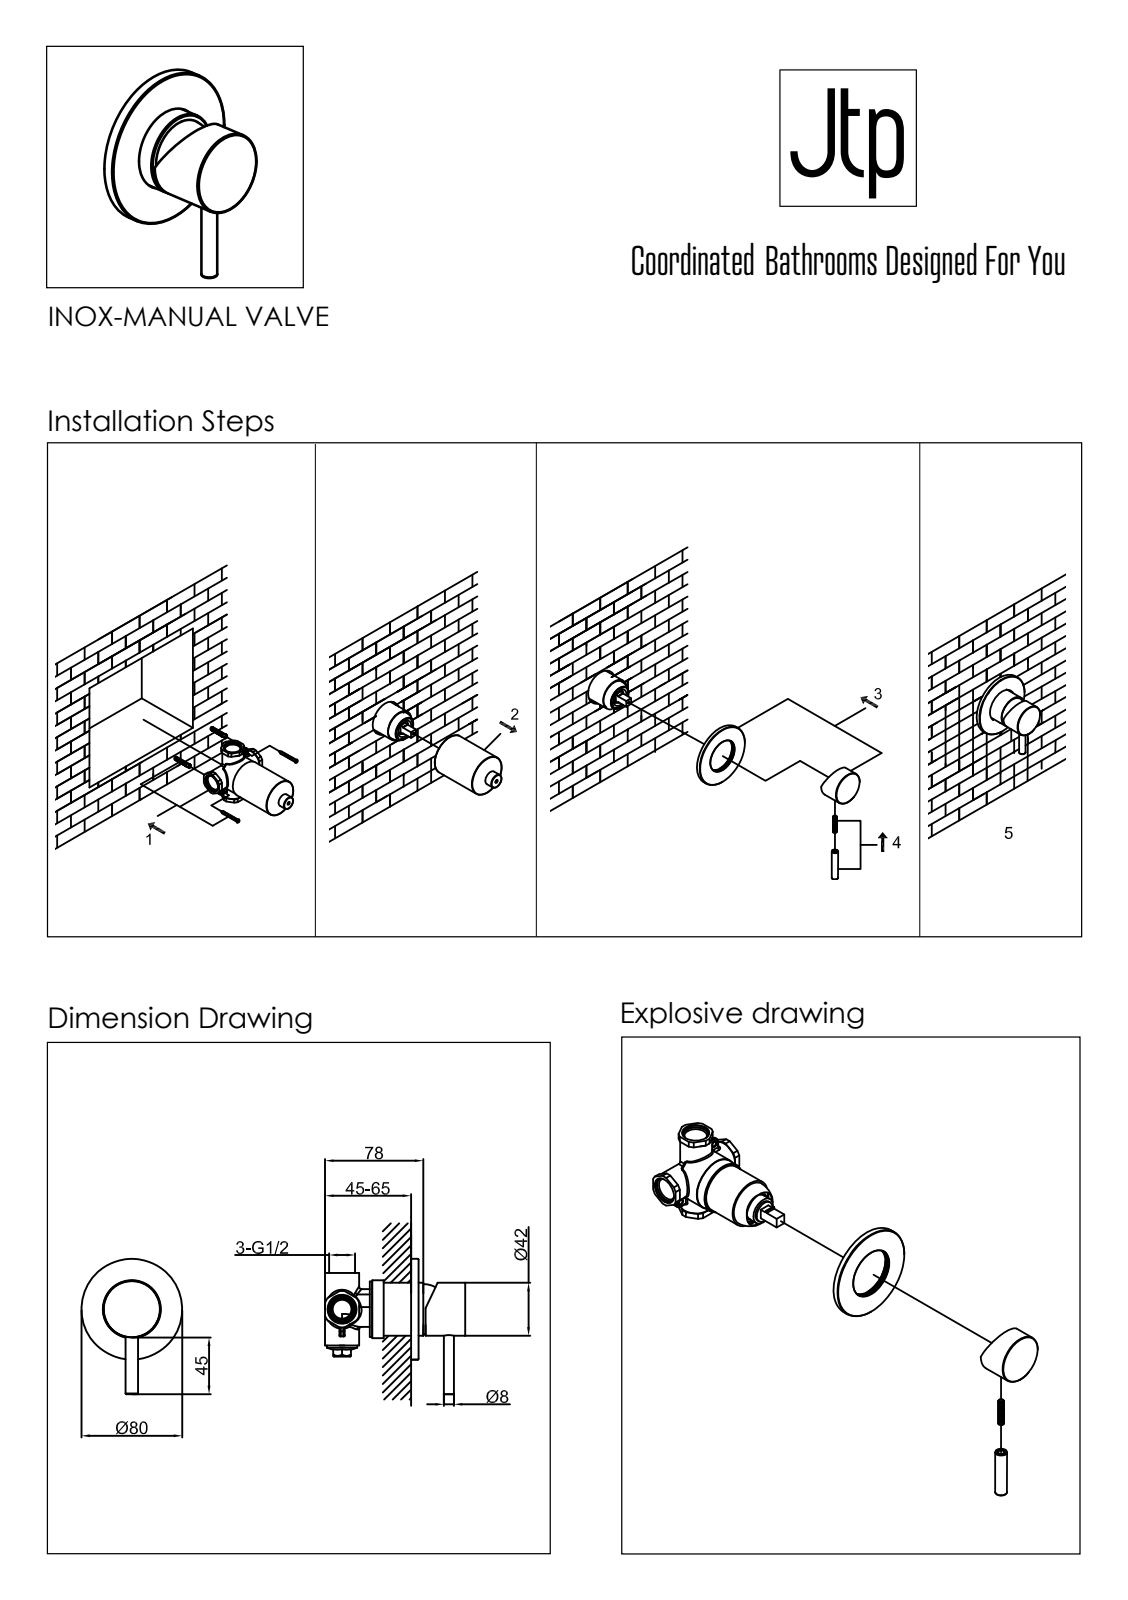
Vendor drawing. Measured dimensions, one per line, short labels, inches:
name: 227
written by: PRO/ENGINEER BY PARAMETRIC TECHNOLOGY CORPORATION, 2012130 (CONFIG_CONTROL_DESIGN)
unit: in
bodies: 2 solids, 28 faces (8 planar, 10 cylindrical, 10 other)
size: 106 × 80 × 49.5
volume: 101 441 in³; area: 21 567 in²
holes: 1× ⌀42.5
bosses: 1× ⌀80, 1× ⌀42, 1× ⌀8
face distances: 9, 49.5, 40.5, 16, 7, 33.5, 18, 2, 31.5
